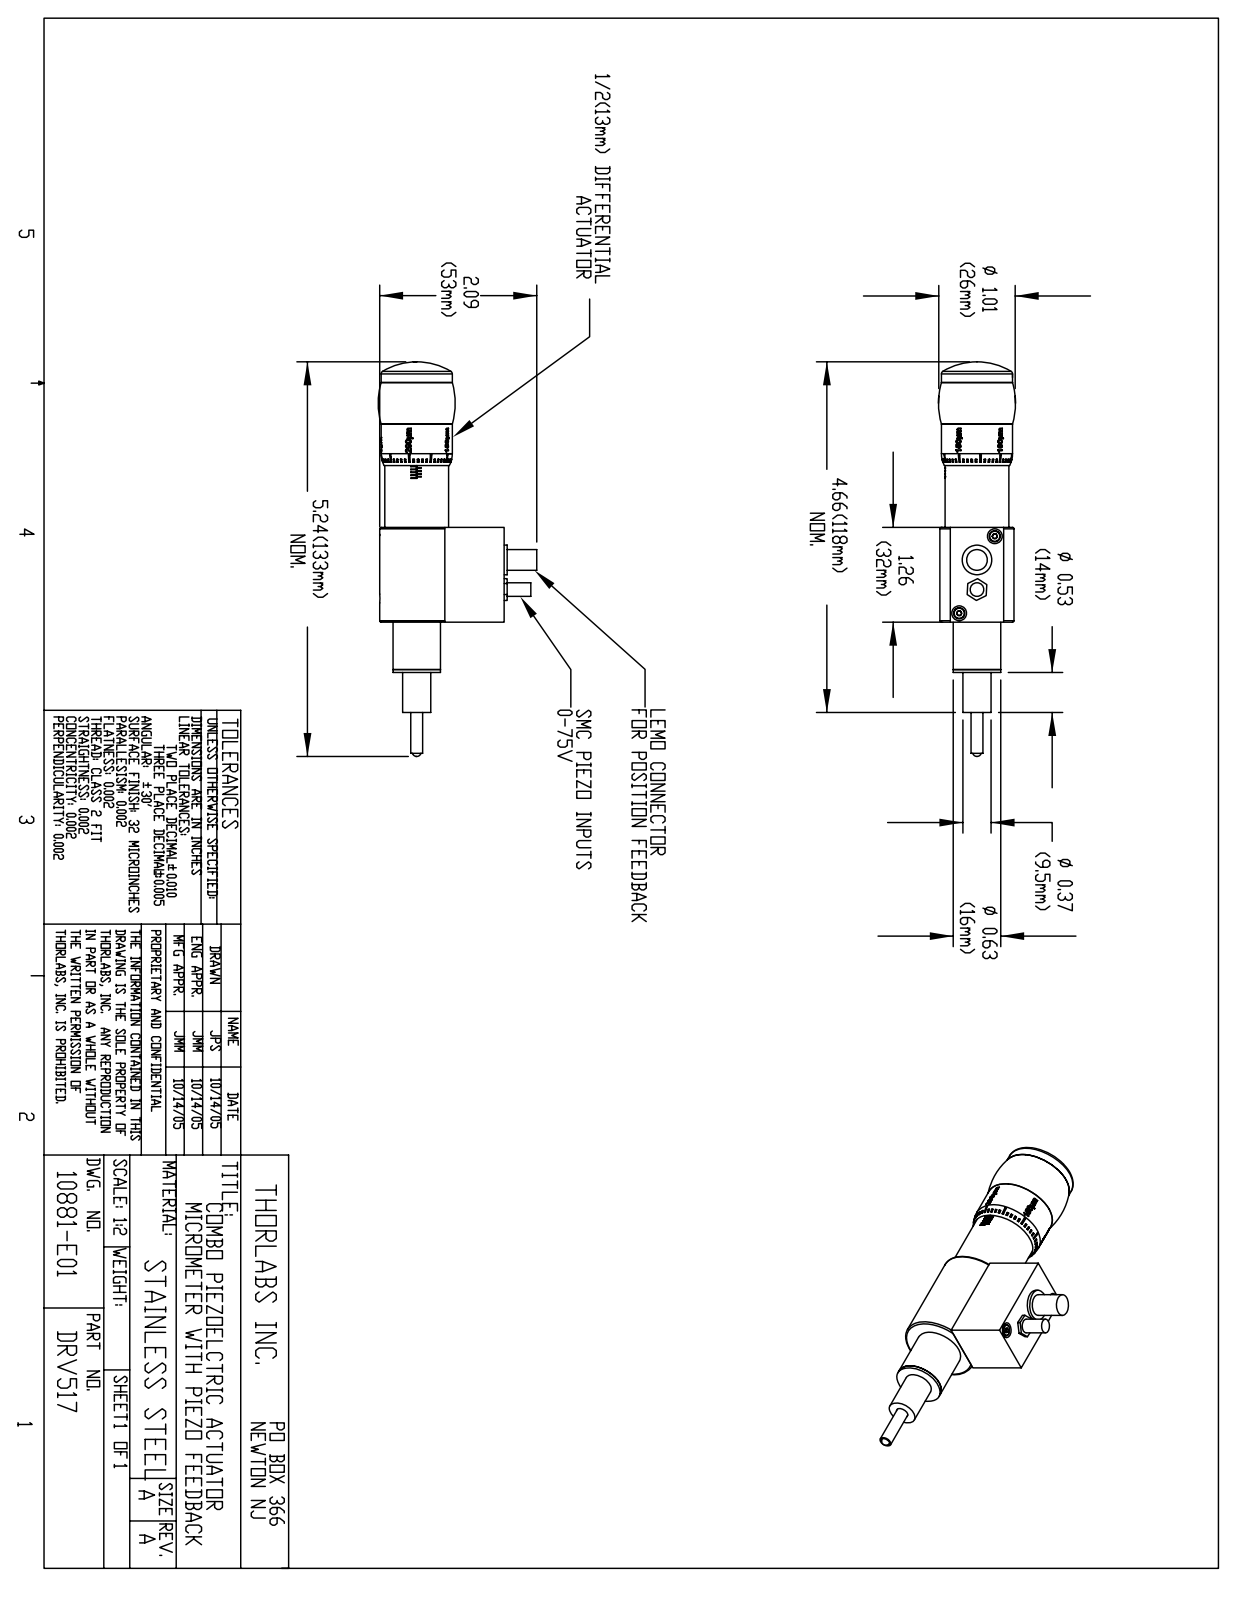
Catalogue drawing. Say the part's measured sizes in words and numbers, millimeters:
The part is named "10881-E0W". Its 3-D file was written by "SolidWorks 2007 (AUTOMOTIVE_DESIGN)". It is 0 solids with 490 faces: 213 planar, 112 cylindrical and 165 other. Overall it measures 133.2 by 53.5 by 26 millimeters. Round holes: 2 of diameter 5, 1 of diameter 2.5, 1 of diameter 3, 1 of diameter 4.2, 1 of diameter 22. Round bosses or shafts: 2 of diameter 3.8, 1 of diameter 24, 1 of diameter 21.5, 1 of diameter 16, 1 of diameter 10, 1 of diameter 9.5, 1 of diameter 7, 1 of diameter 4.6. Partial cylindrical surfaces (rounded edges, fillets, slot ends): 1 of radius 10.7, 1 of radius 11.5, 1 of radius 12.5. The main face-to-face distances are 18, 32, 49, 17, 20, 1, 21, 62.5, 30.5, 13.5. The hole center spacings are 7.8, 21.8, 28.7.
